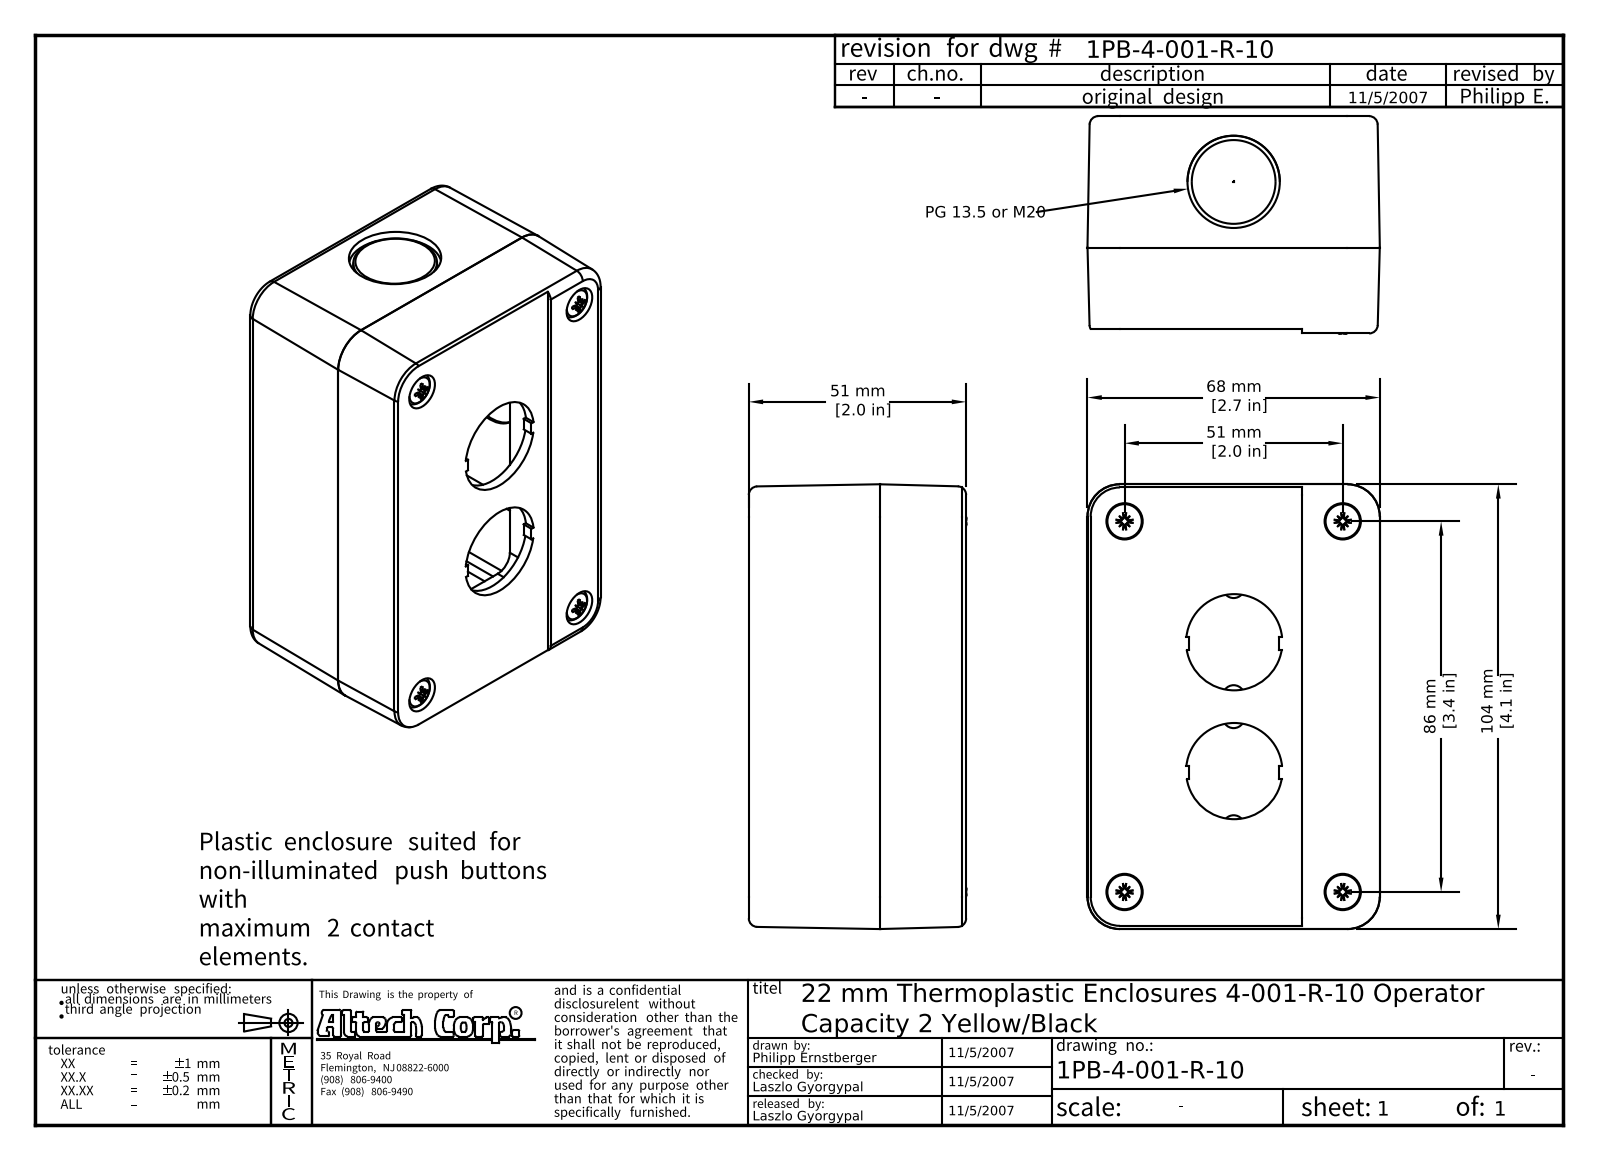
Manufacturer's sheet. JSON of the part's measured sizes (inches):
{"part_name": "4-001-R-10; Teknic_enclousure_back; Teknic_enclousure; NF EN ISO 7045 - Z M4 x 30 - 4.8 - Z", "step_written_by": "Autodesk Inventor 2008 (AUTOMOTIVE_DESIGN)", "units": "inches", "bodies": {"solids": 6, "faces": 559, "planar": 238, "cylindrical": 145, "other": 176}, "overall_size": [4.078, 2.68, 1.994], "volume_in3": 5.11, "surface_area_in2": 147.6, "round_holes": [[0.059, 8], [0.098, 4], [0.175, 2], [0.333, 2], [0.846, 2], [0.882, 2], [0.787, 1]], "round_bosses_or_shafts": [[0.157, 4], [0.143, 4], [0.768, 2], [0.49, 2]], "partial_cylinders_radius": [[0.028, 13], [0.118, 12], [0.049, 8], [0.079, 8], [0.173, 8], [0.177, 8], [0.063, 4], [0.098, 4]], "face_to_face_distances": [0.059, 0.063, 0.079, 0.122, 1.854, 1.791, 1.953, 1.894, 1.89, 1.831], "hole_center_spacings": [0.263, 0.291, 0.512, 1.085, 1.085, 2.261, 1.192, 1.193]}
